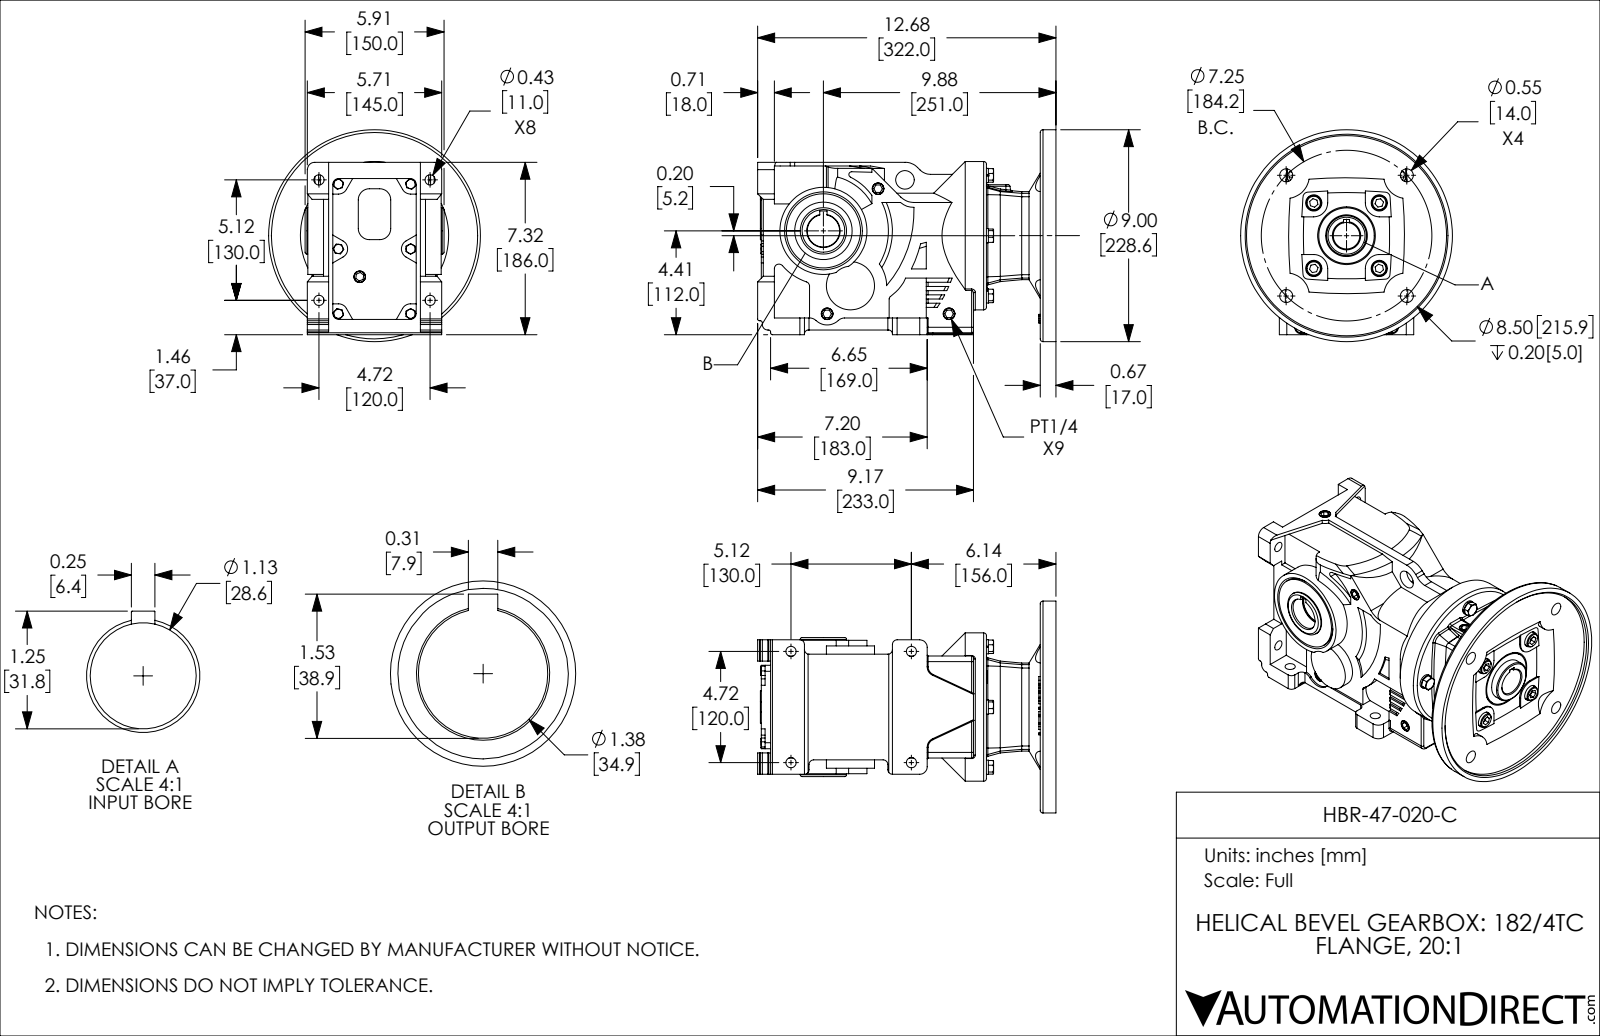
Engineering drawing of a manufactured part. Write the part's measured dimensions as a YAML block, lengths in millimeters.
part_name: "HBR-47-020-C"
step_written_by: "SolidWorks 2018 (AUTOMOTIVE_DESIGN)"
units: millimeters
bodies: {solids: 1, faces: 1036, planar: 498, cylindrical: 268, other: 270}
overall_size: [322, 228.6, 228.6]
volume: 5714000
surface_area: 369500
round_holes:
  - {diameter: 11, count: 8}
  - {diameter: 8.2, count: 4}
  - {diameter: 9, count: 4}
  - {diameter: 14, count: 4}
  - {diameter: 17.5, count: 4}
  - {diameter: 20, count: 1}
  - {diameter: 28.6, count: 1}
  - {diameter: 34.9, count: 1}
  - {diameter: 36, count: 1}
  - {diameter: 37, count: 1}
  - {diameter: 215.9, count: 1}
round_bosses_or_shafts:
  - {diameter: 16, count: 4}
  - {diameter: 15.4, count: 4}
  - {diameter: 8, count: 4}
  - {diameter: 228.6, count: 1}
  - {diameter: 160, count: 1}
  - {diameter: 94, count: 1}
  - {diameter: 80, count: 1}
  - {diameter: 60, count: 1}
partial_cylinders:
  - {radius: 2, count: 15}
  - {radius: 5, count: 10}
  - {radius: 10, count: 10}
  - {radius: 12, count: 9}
  - {radius: 4, count: 6}
  - {radius: 1, count: 5}
  - {radius: 17.5, count: 5}
  - {radius: 6.5, count: 4}
face_to_face_distances: [11.9, 5, 110, 17, 2, 3, 4, 10, 312.9, 301]
hole_center_spacings: [46.2, 65.1, 104.8, 106.4, 145.5, 130, 42.1, 50]
